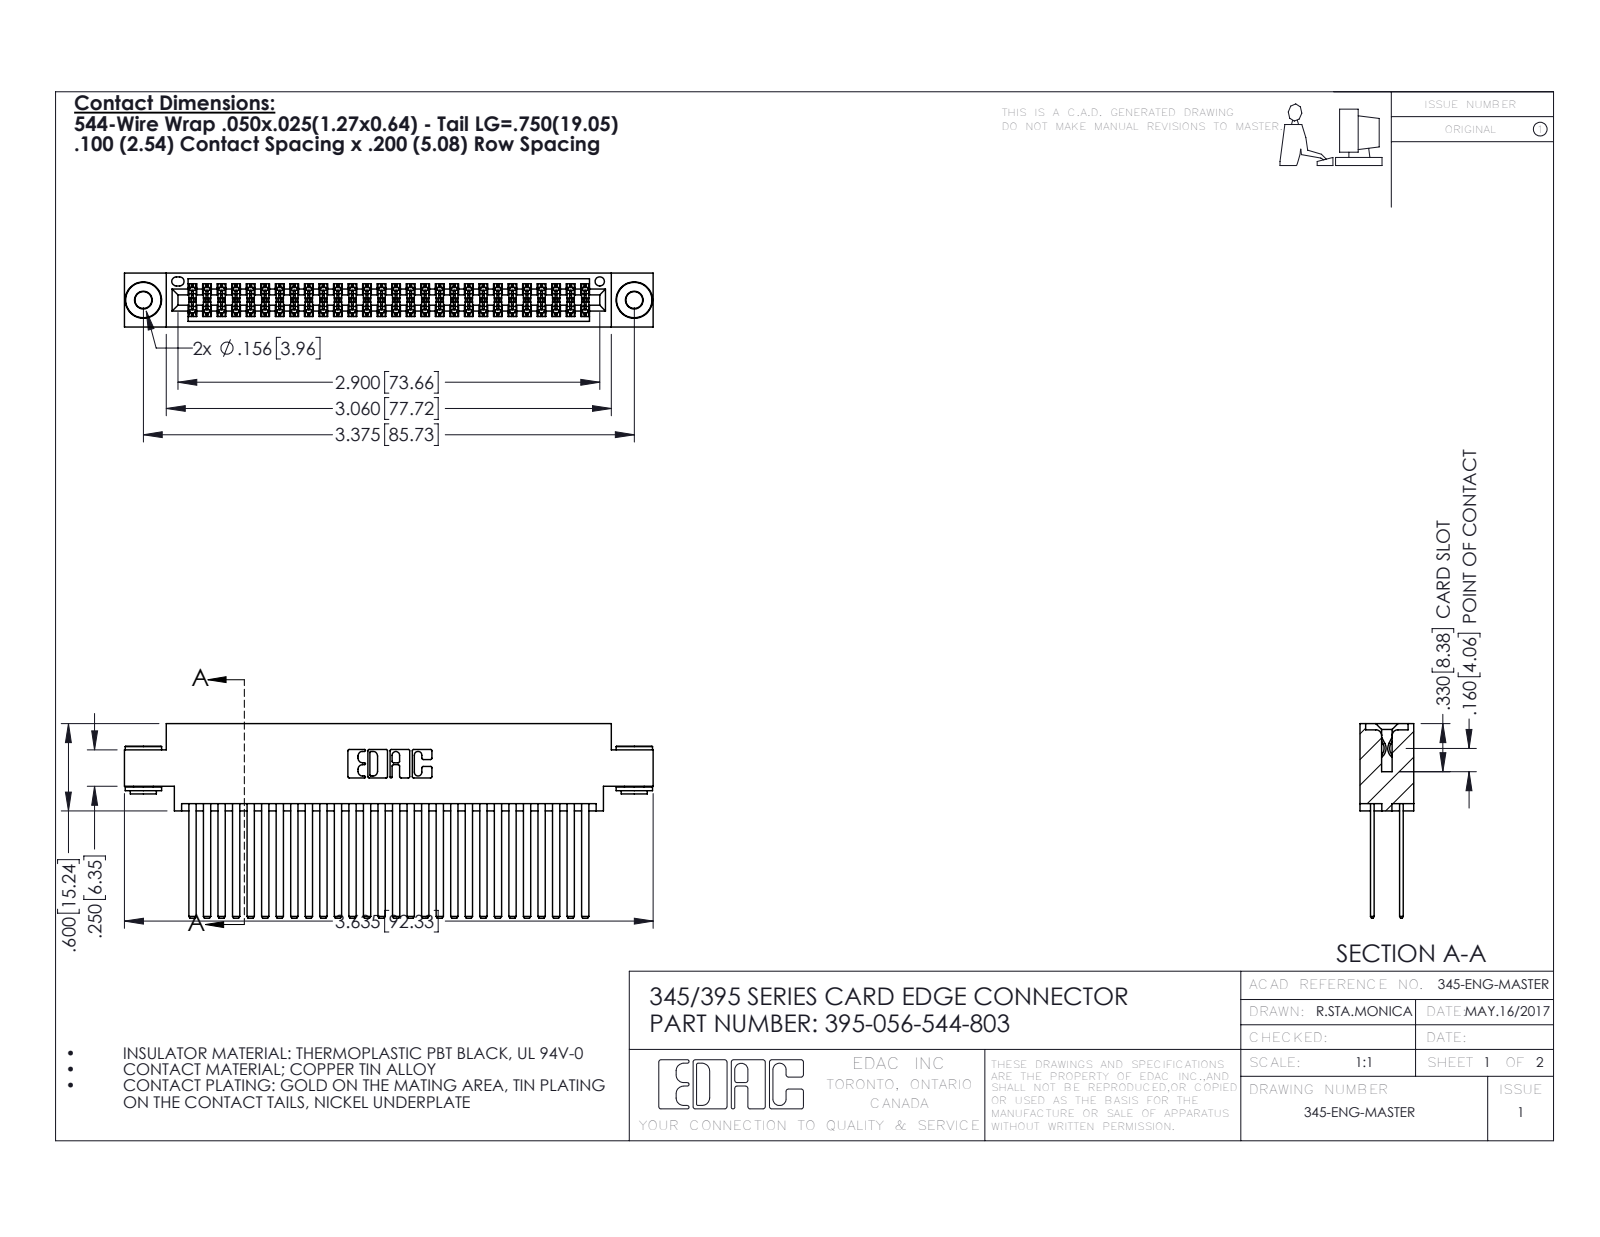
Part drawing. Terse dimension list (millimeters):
name: 395-056-544-803; 345 Part_0.170 Offset - 0.156 Dia-TH; 345-250-002_345-250-002-102; 345-292-001_345-293-144
written by: SolidWorks 2016 (CONFIG_CONTROL_DESIGN)
unit: mm
bodies: 59 solids, 2632 faces (1718 planar, 906 cylindrical, 8 other)
size: 92.3 × 34 × 9.4
volume: 9 540 mm³; area: 16 460 mm²
holes: 2× ⌀2.9, 2× ⌀4, 1× ⌀1.6
bosses: 2× ⌀6.4, 2× ⌀4.6, 2× ⌀3.5
rounds: 84× R0.2, 22× R0.3, 6× R0.2, 6× R0.8, 3× R0.7, 2× R0.4, 2× R0.5, 2× R0.6
face distances: 5.1, 0.6, 1.8, 7.6, 2.5, 6.9, 5.7, 4.4, 9.4, 3.8
hole spacings: 6.9, 79.8, 85.7
